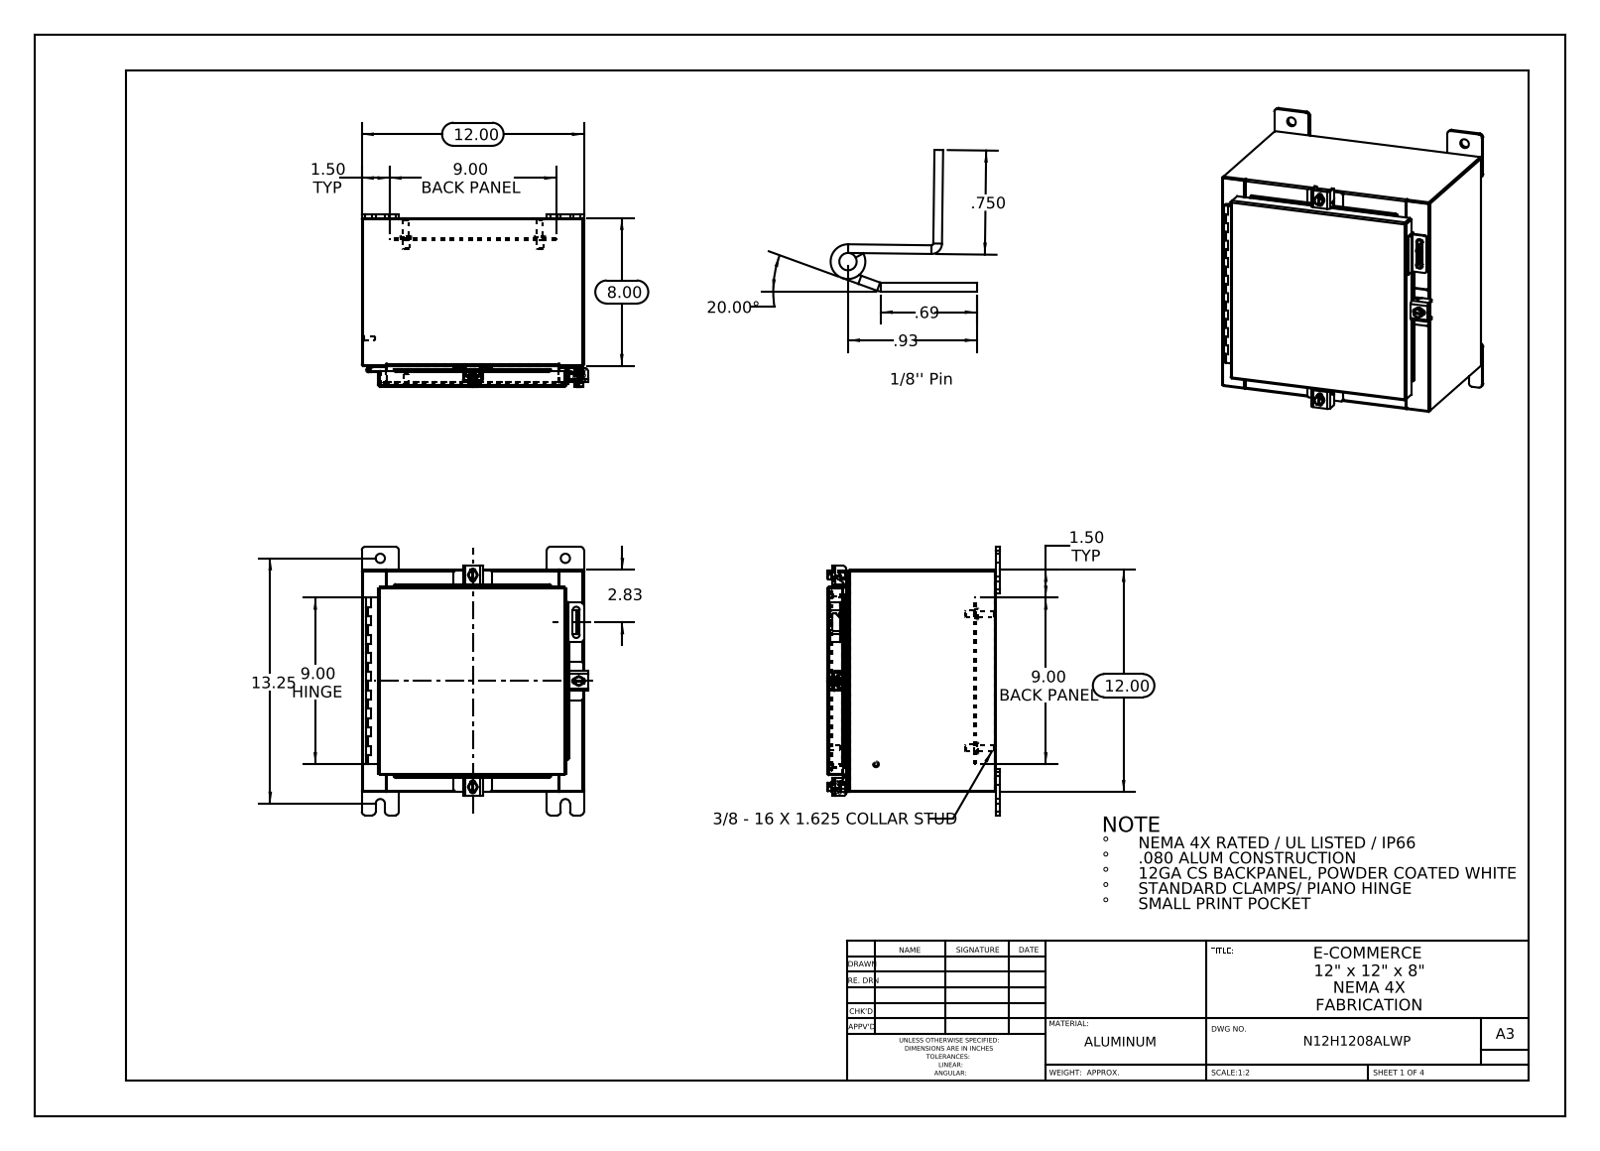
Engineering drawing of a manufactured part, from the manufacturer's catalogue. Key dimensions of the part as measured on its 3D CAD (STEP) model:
Part name (STEP PRODUCT): N12H1208ALWP Clamp Assembly; N12H1208ALWP Hinge Cover Side; N12H1208ALWP Padlock Hasp; N12H1208ALWP Backpanel (+8 more)
STEP written by: SolidWorks 2014 (CONFIG_CONTROL_DESIGN)
Units: inches
Bodies: 34 solids, 1080 faces (578 planar, 418 cylindrical, 84 other)
Overall size (bounding box): 14.5 × 12.211 × 9.313
Volume: 71.59 in³ · Surface area: 1 832 in²
Round holes (diameter × count): ⌀0.5 ×8, ⌀0.213 ×3, ⌀0.26 ×3, ⌀0.125 ×2
Round bosses / shafts (diameter × count): ⌀0.625 ×4, ⌀0.375 ×4, ⌀0.33 ×4, ⌀0.25 ×4, ⌀0.5 ×3, ⌀0.399 ×3, ⌀0.315 ×2, ⌀0.236 ×2
Partial cylindrical surfaces — rounded edges, fillets, slot ends (radius × count): R0.19 ×24, R0.013 ×23, R0.088 ×21, R0.06 ×18, R0.125 ×10, R0.019 ×6, R0.1 ×6, R0.12 ×6
Main face-to-face distances: 0.075, 11.925, 9.039, 11.85, 12, 7.925, 1.114, 8.964, 9.114, 1
Hole centre spacings: 4.19, 10.029, 2.226, 3.3, 5.012, 5.08, 7.25, 7.25
